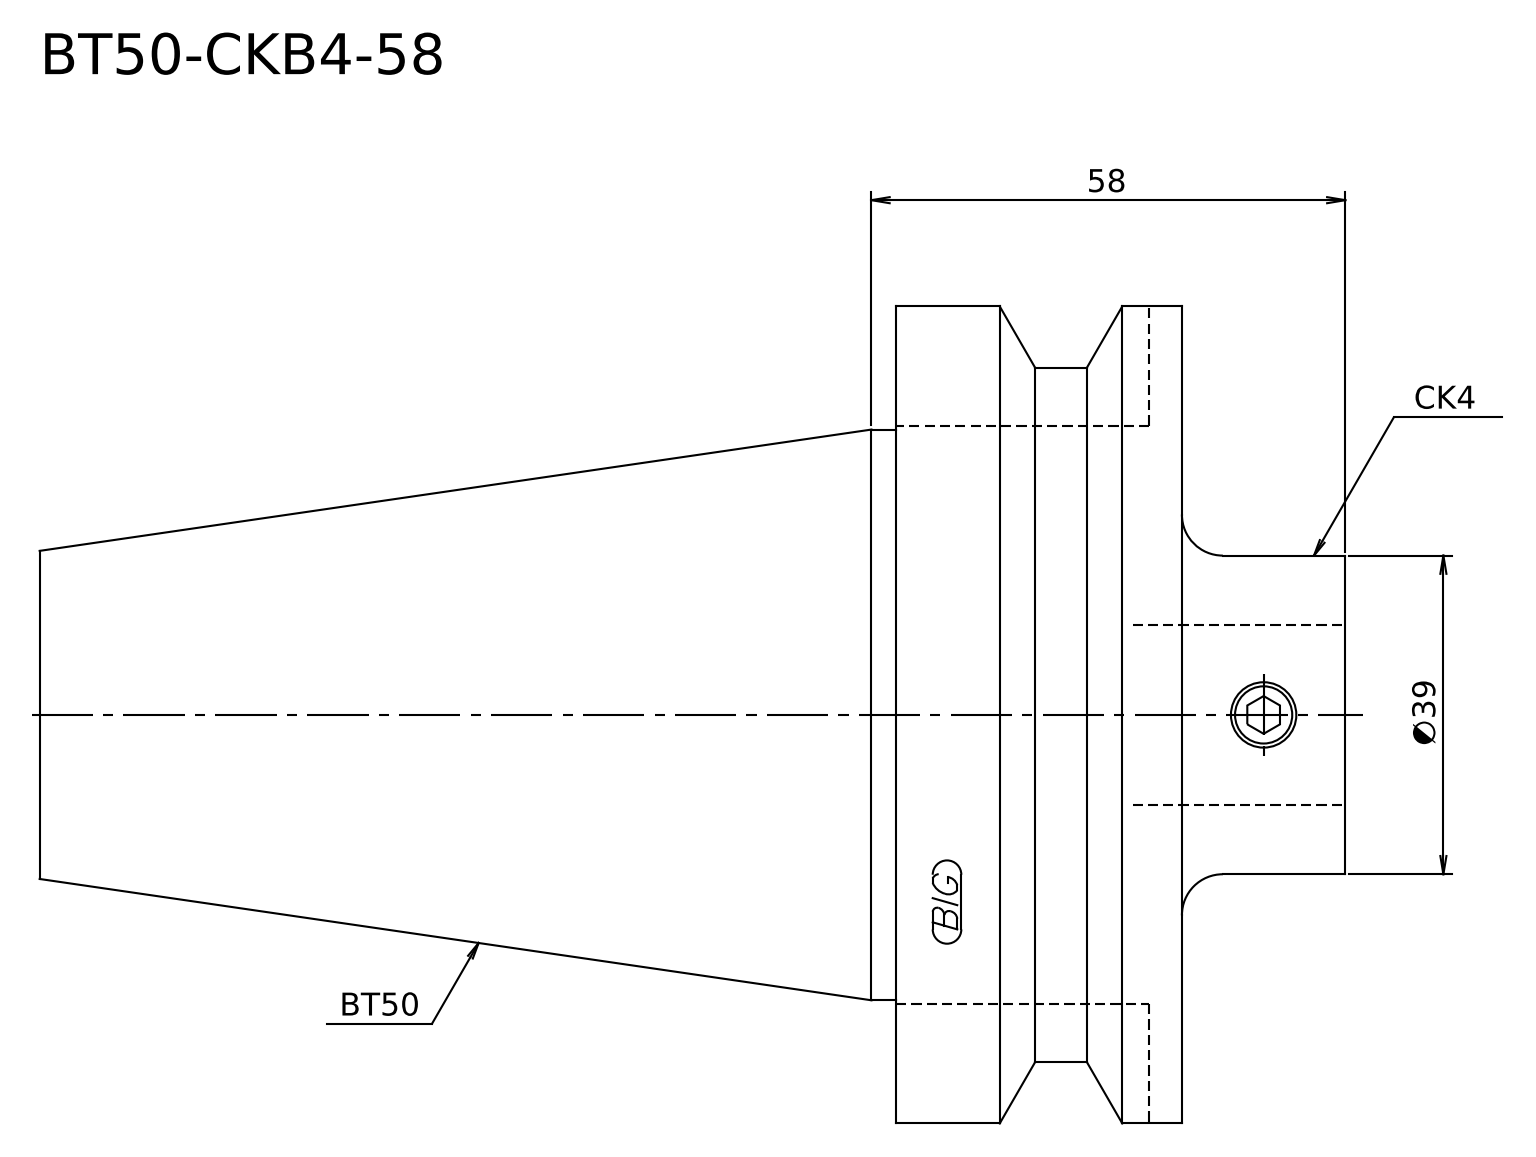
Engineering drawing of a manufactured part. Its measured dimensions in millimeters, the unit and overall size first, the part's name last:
Units: millimetres
Overall size (bounding box): 159.8 × 100 × 100
Round bosses / shafts (diameter × count): ⌀100 ×1, ⌀85 ×1, ⌀69.85 ×1, ⌀39 ×1
Main face-to-face distances: 35, 139.8, 104.8, 20, 55, 159.8
Volume: 536 200 mm³ · Surface area: 46 712 mm²
Bodies: 1 solid, 13 faces (4 planar, 5 cylindrical, 4 other)
STEP written by: Kubotek KeyCreator V8.5.1 (14335) (CONFIG_CONTROL_DESIGN)
